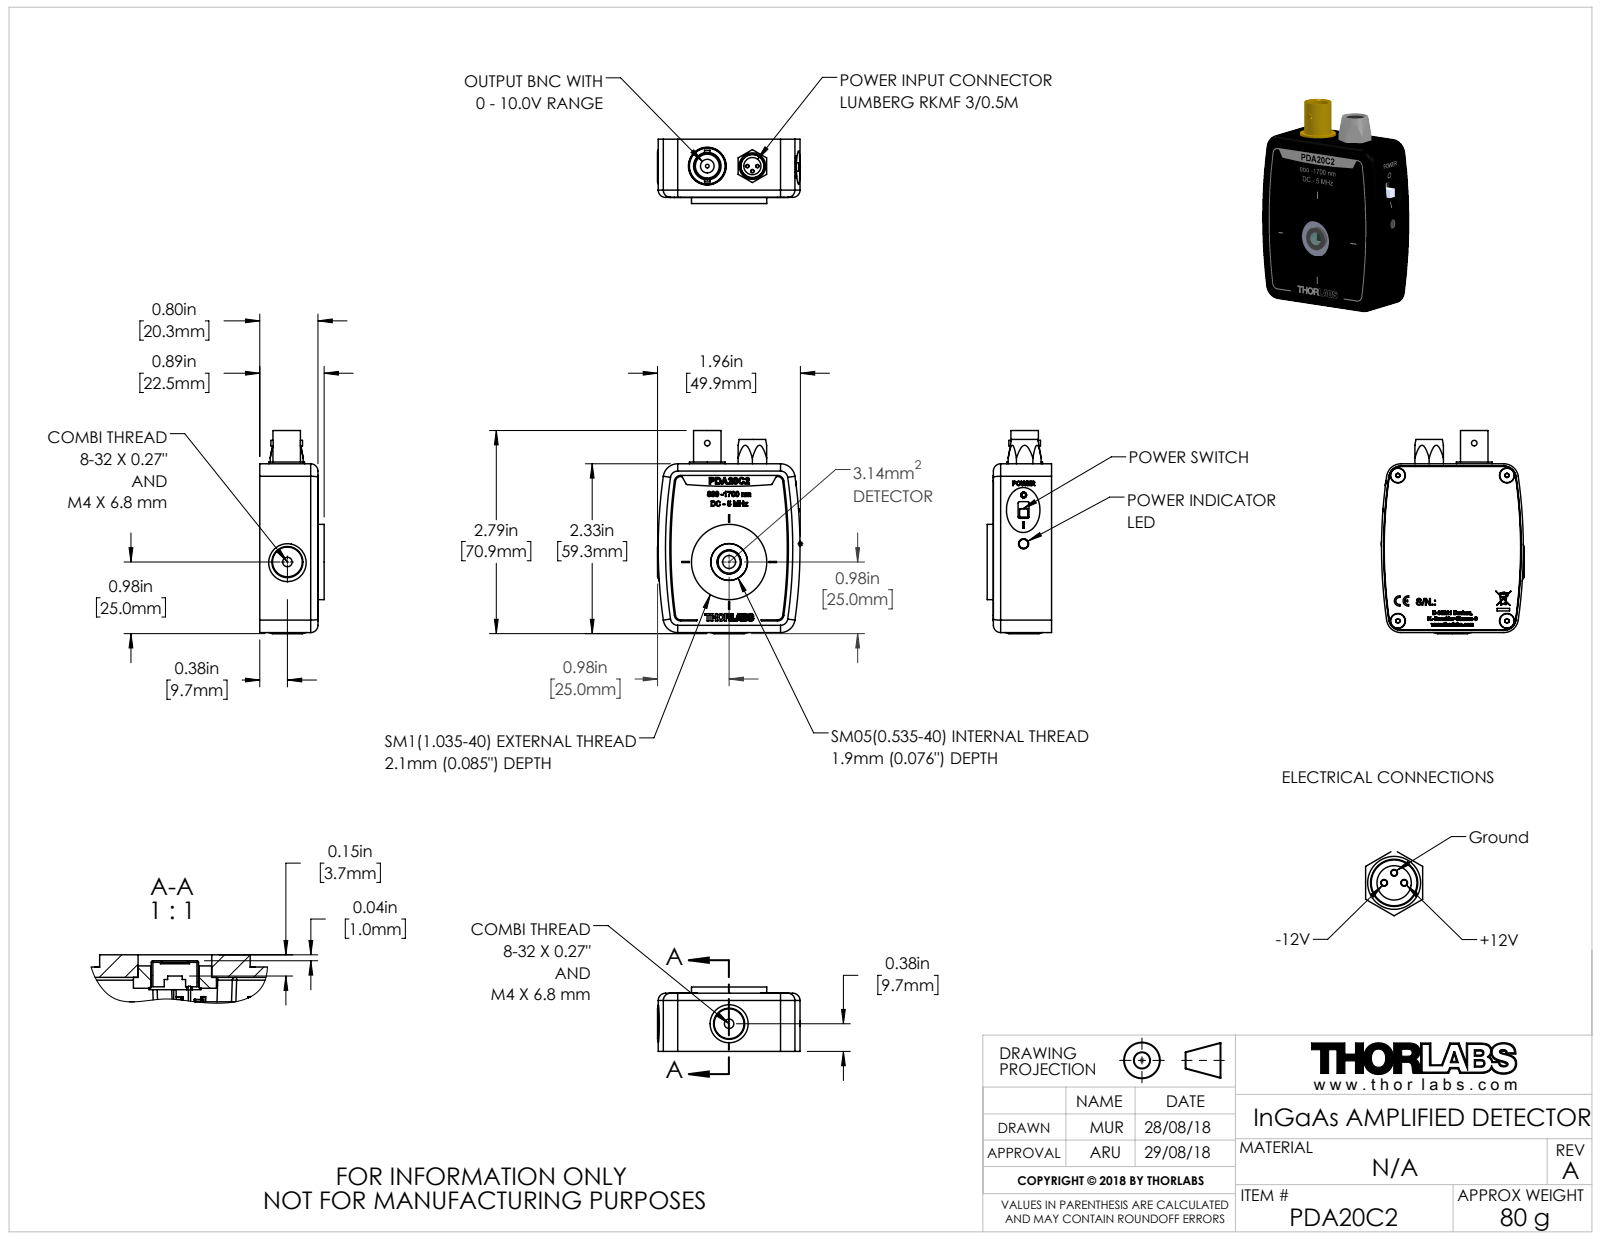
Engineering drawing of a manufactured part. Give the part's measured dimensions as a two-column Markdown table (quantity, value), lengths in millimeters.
| quantity | value |
| --- | --- |
| part name | PDA20C2_web |
| STEP written by | SolidWorks 2018 (AUTOMOTIVE_DESIGN) |
| units | millimeters |
| bodies | 0 solids, 612 faces (316 planar, 100 cylindrical, 196 other) |
| overall size | 70.9 × 49.89 × 22.48 |
| round holes (diameter × count) | 1 × 3, 3.3 × 2, 1.27 × 1, 3.56 × 1, 4.5 × 1, 8 × 1, 8.25 × 1, 8.33 × 1, 8.4 × 1, 12.88 × 1 |
| round bosses / shafts (diameter × count) | 5 × 4, 26.29 × 1, 12.5 × 1, 9.6 × 1, 8.25 × 1, 6 × 1, 2.03 × 1, 1.93 × 1 |
| partial cylindrical surfaces (radius × count) | 0.51 × 4, 1.85 × 4, 4.06 × 4, 5.08 × 4, 177.8 × 4, 2.54 × 2, 173.35 × 2, 173.74 × 2 |
| main face-to-face distances | 1.5, 16.94, 18.44, 20.22, 1.78, 18.72, 58.93, 2.16, 3.94, 20.88 |
| hole center spacings | 1.75, 2.47, 3.5, 6.35, 6.38, 7.62, 8.13, 8.27 |
